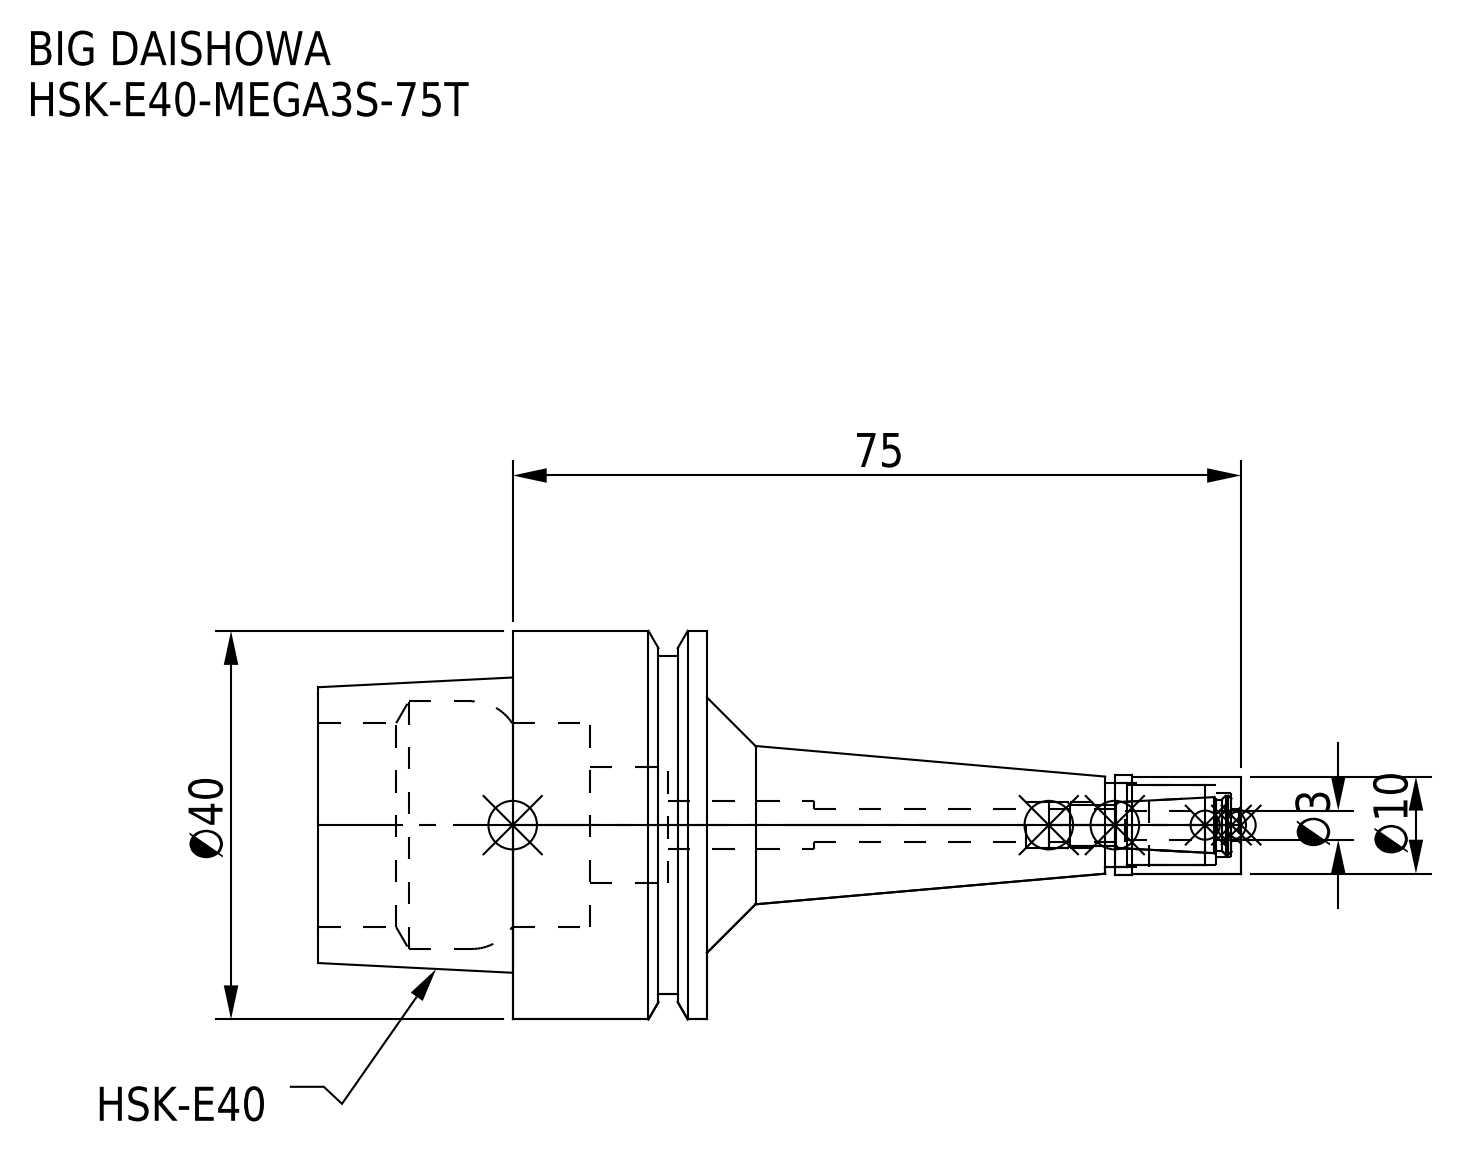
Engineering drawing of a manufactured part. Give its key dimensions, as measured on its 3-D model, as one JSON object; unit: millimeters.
{"part_name": "HE40MS03075T-030_ASM.stp; MGN3S_1.stp; HSK-E40-MEGA3S-75T-030.stp; HSK-E40-MEGA3S-75T-030-FreeParts (+3 more)", "step_written_by": "SolidWorks 2019 (CONFIG_CONTROL_DESIGN)", "units": "millimeters", "bodies": {"solids": 2, "faces": 74, "planar": 18, "cylindrical": 38, "other": 18}, "overall_size": [95, 40, 40], "volume_mm3": 32557, "surface_area_mm2": 12985, "round_holes": [[3.3, 1], [3.4, 1], [4.7, 1], [5, 1], [6.6, 1], [8.2, 1], [8.7, 1], [12, 1], [21, 1], [25.5, 1]], "round_bosses_or_shafts": [[40, 1], [34.8, 1], [10.3, 1], [10, 1]], "face_to_face_distances": [20, 40, 12.05, 7.95, 27.95, 8, 4.05, 15.95, 35.95, 5]}
